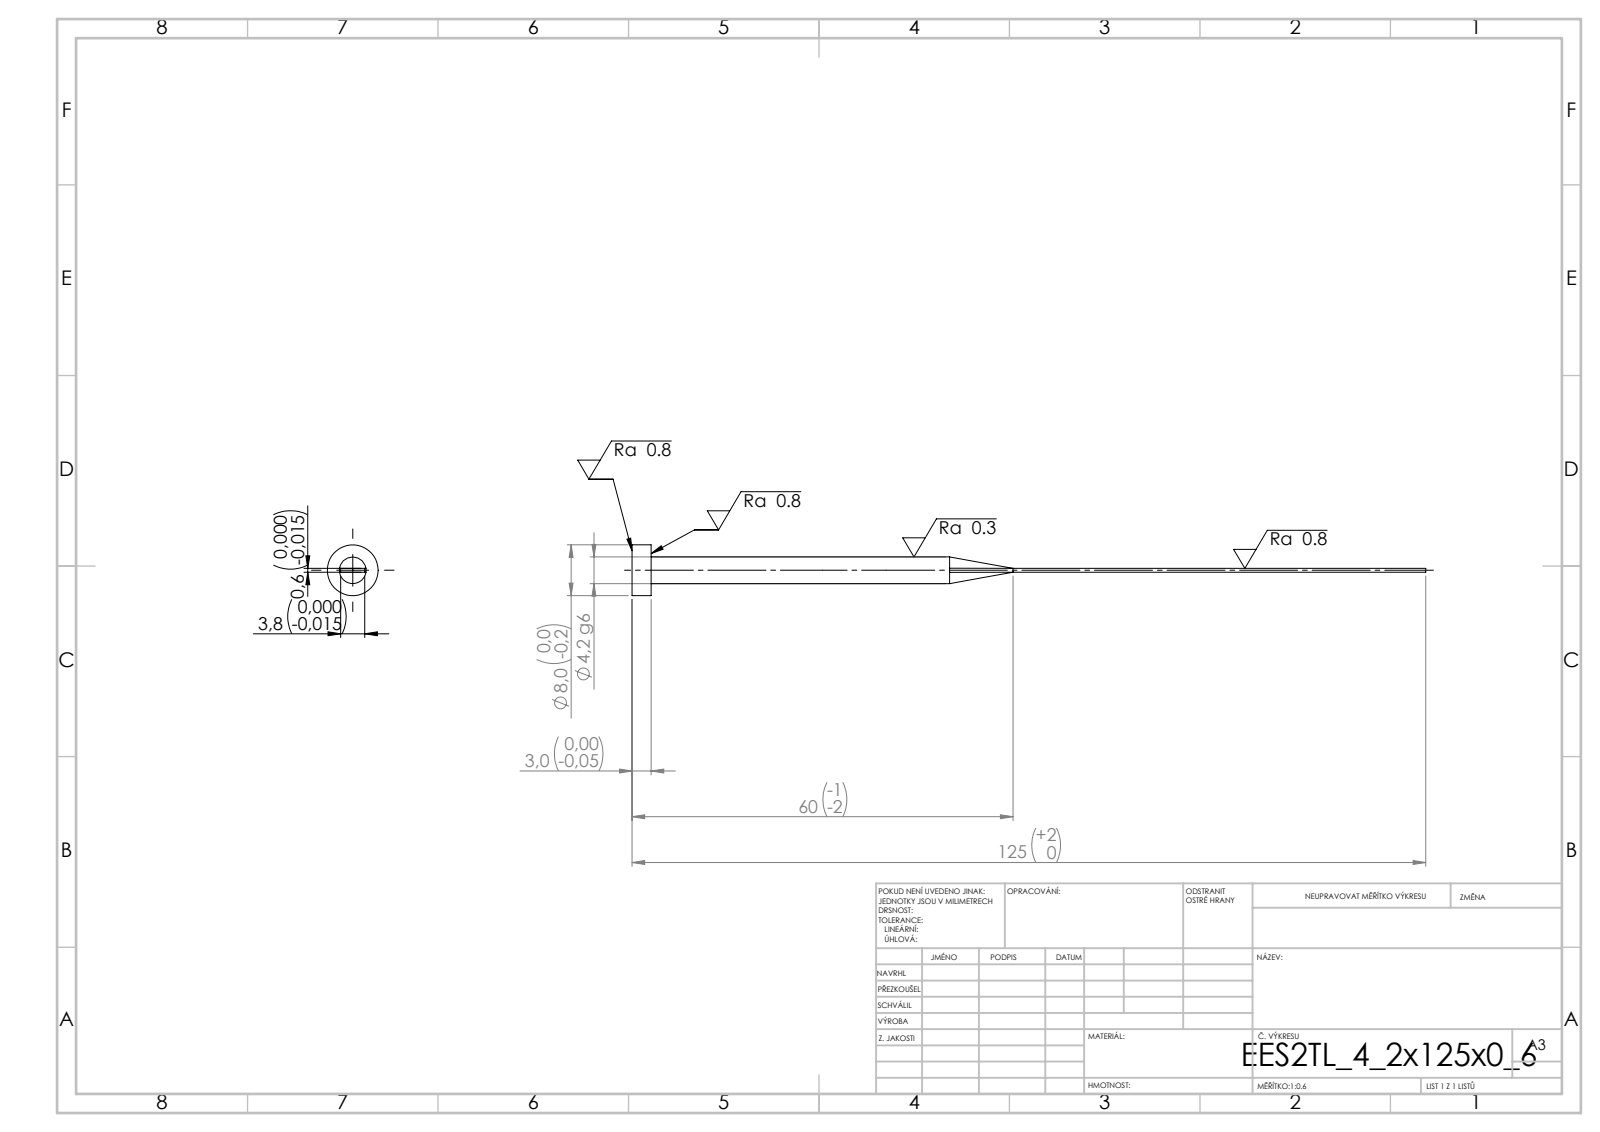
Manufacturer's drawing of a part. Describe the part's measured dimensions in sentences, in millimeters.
Its 3-D file was written by "SolidWorks 2019 (CONFIG_CONTROL_DESIGN)". It is 1 solid with 15 faces: 7 planar, 4 cylindrical and 4 other. Overall it measures 125 by 8 by 8 millimeters. Its volume is 1 026 cubic millimeters and its surface area 1 462 square millimeters. Round bosses or shafts: 1 of diameter 8, 1 of diameter 4.2. The main face-to-face distances are 0.6, 3.8, 3, 125, 122.
